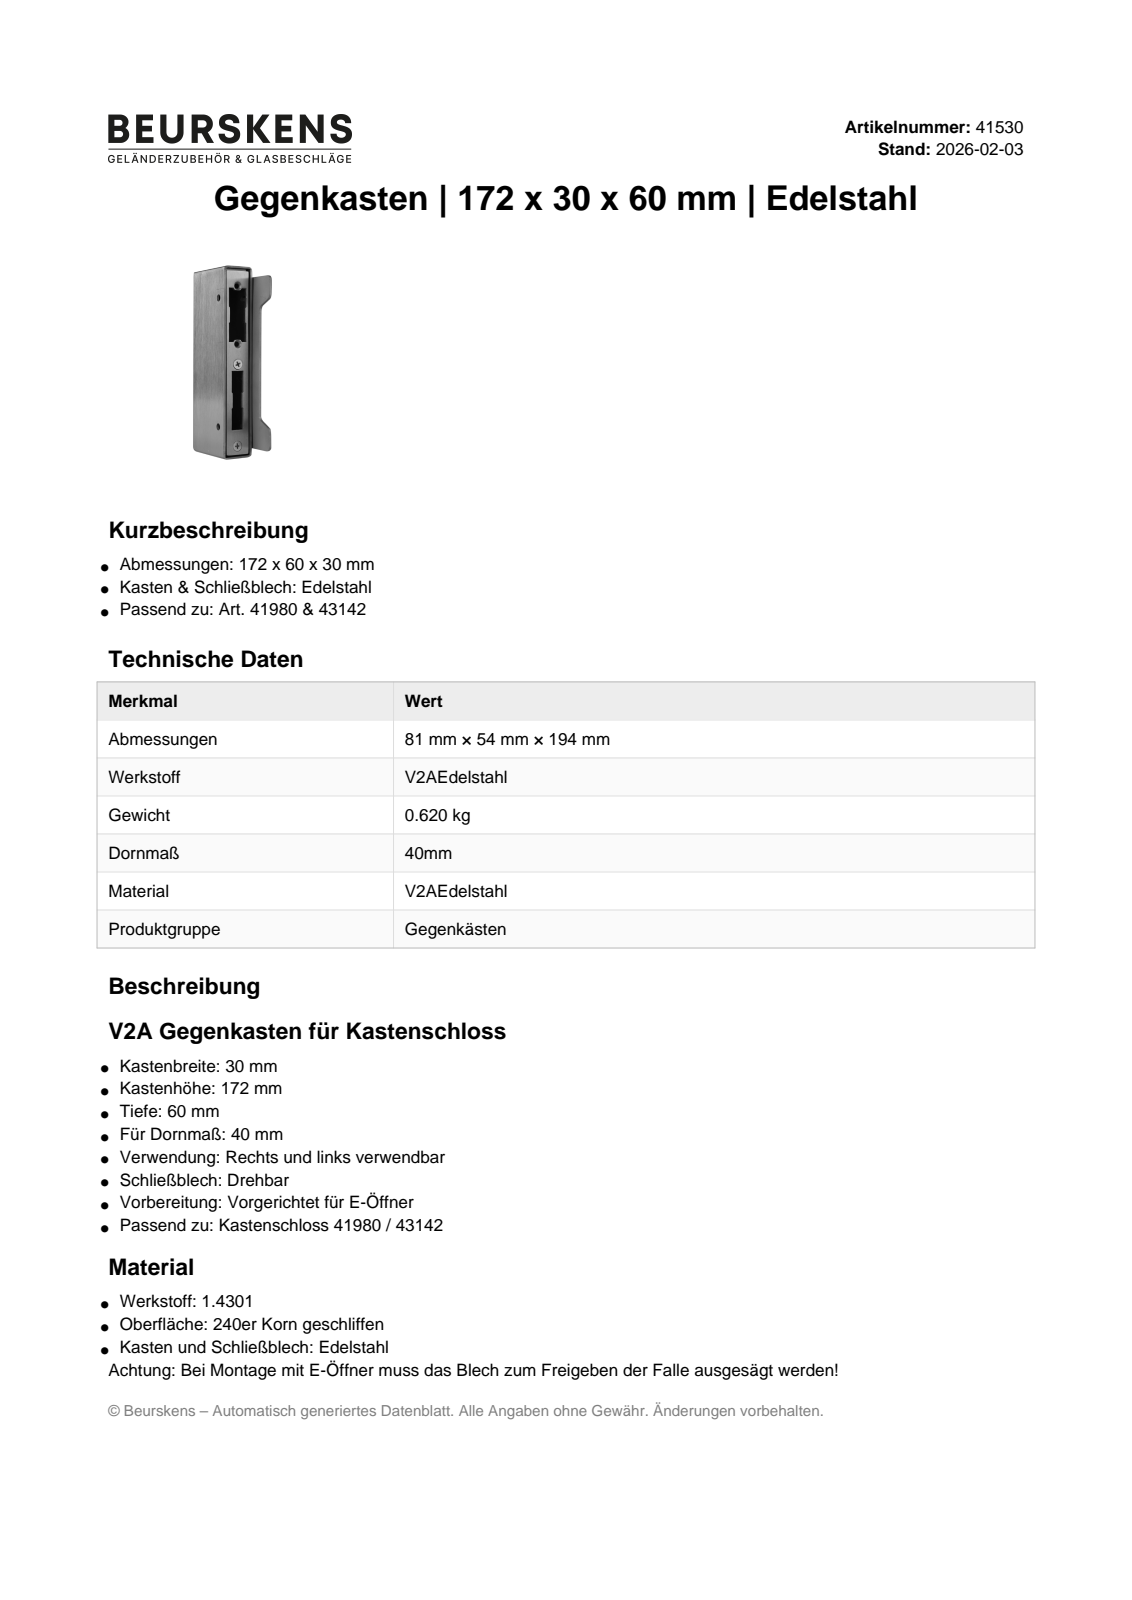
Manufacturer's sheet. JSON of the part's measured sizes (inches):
{"part_name": "41530; 41530_Kasten; 41524; Anschlagblech (+1 more)", "step_written_by": "Autodesk Inventor 2022 (AUTOMOTIVE_DESIGN)", "units": "inches", "bodies": {"solids": 5, "faces": 117, "planar": 73, "cylindrical": 34, "other": 10}, "overall_size": [6.772, 3.346, 1.302], "volume_in3": 5.795, "surface_area_in2": 118.9, "round_holes": [[0.177, 2], [0.197, 2], [0.217, 2], [0.236, 2]], "round_bosses_or_shafts": [[0.197, 4]], "partial_cylinders_radius": [[0.079, 12], [0.197, 8]], "face_to_face_distances": [0.098, 1.083, 1.181, 0.984, 0.118, 0.1, 1.281, 1.183, 0.018, 0.199], "hole_center_spacings": [0.709, 2.047, 2.756, 2.874, 3.583, 4.528, 5.63]}
